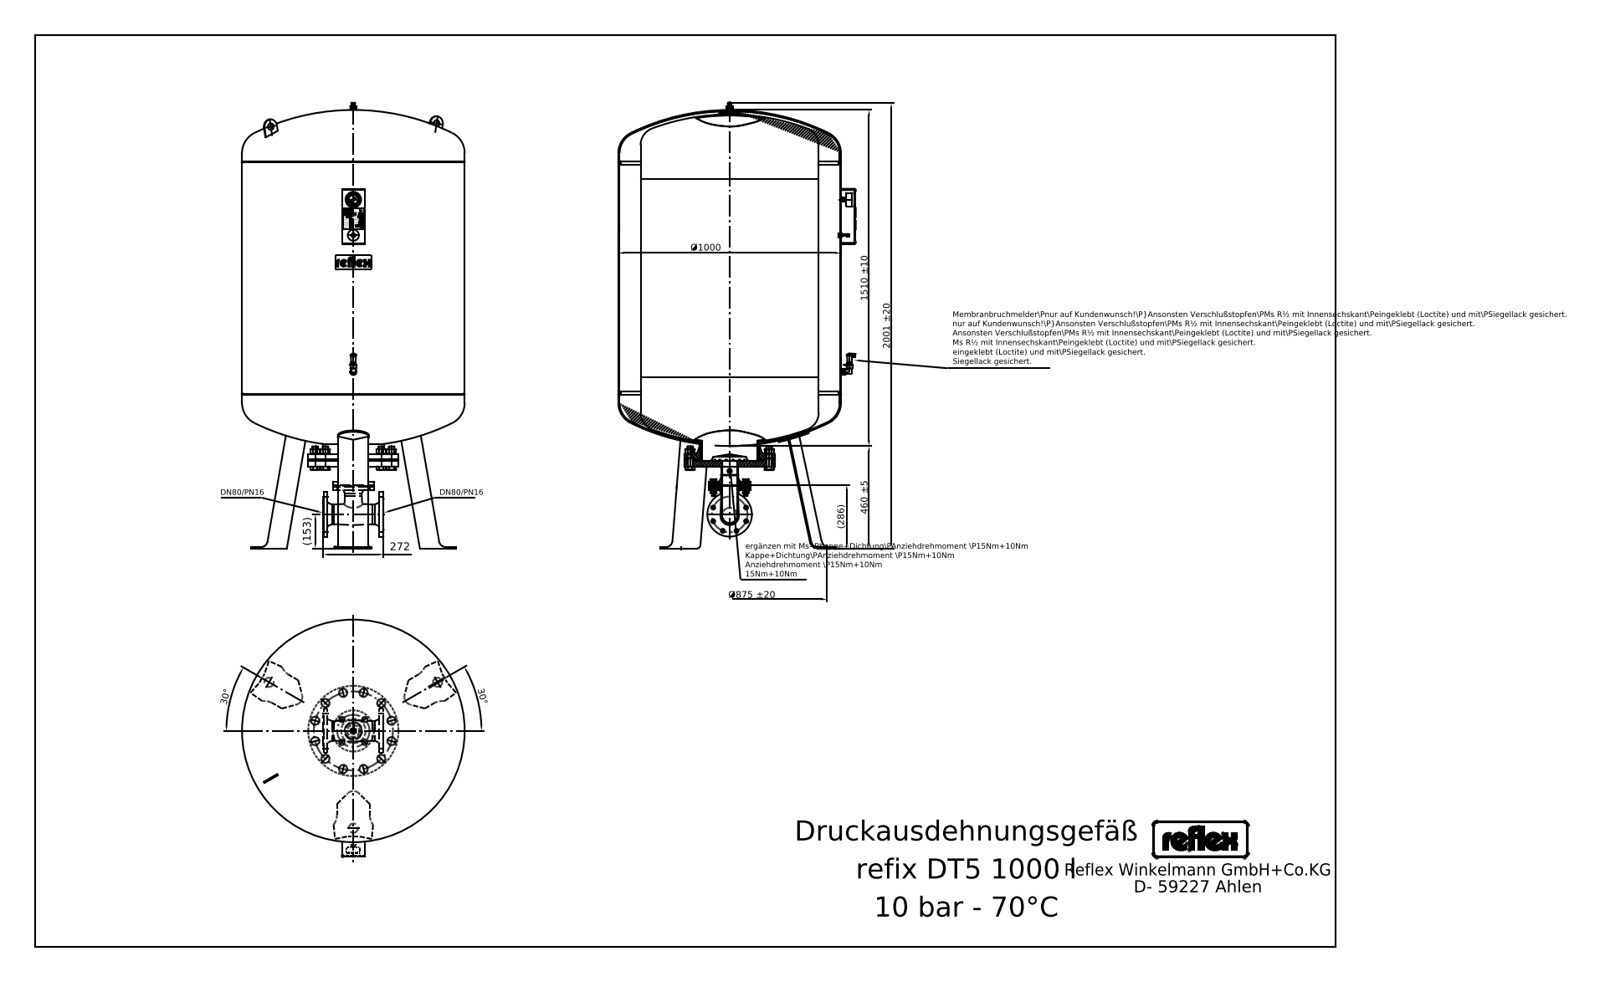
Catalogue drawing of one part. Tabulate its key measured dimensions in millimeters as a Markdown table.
| quantity | value |
| --- | --- |
| STEP written by | Mechanical Desktop 2008 (CONFIG_CONTROL_DESIGN) |
| units | millimeters |
| bodies | 31 solids, 793 faces (417 planar, 193 cylindrical, 183 other) |
| overall size | 2000 × 1066 × 1000 |
| volume | 1 093 000 000 mm³ |
| surface area | 10 690 000 mm² |
| round holes (diameter × count) | 19 × 8, 10 × 1, 30 × 1, 50 × 1, 69 × 1, 88.9 × 1, 260.4 × 1 |
| round bosses / shafts (diameter × count) | 16 × 17, 28 × 2, 26 × 2, 20 × 2, 1000 × 1, 405 × 1, 273 × 1, 200 × 1 |
| partial cylindrical surfaces (radius × count) | 25 × 18, 5.62 × 4, 2.25 × 3, 9 × 3, 1 × 2, 3.84 × 2, 5 × 2, 6.75 × 2 |
| main face-to-face distances | 1075, 26, 274.5, 1349.5, 300.5, 1375.5, 31, 57, 243.5, 1318.5 |
| hole center spacings | 80, 113.13, 61.22, 61.24, 147.81, 147.82, 160, 82.33 |
